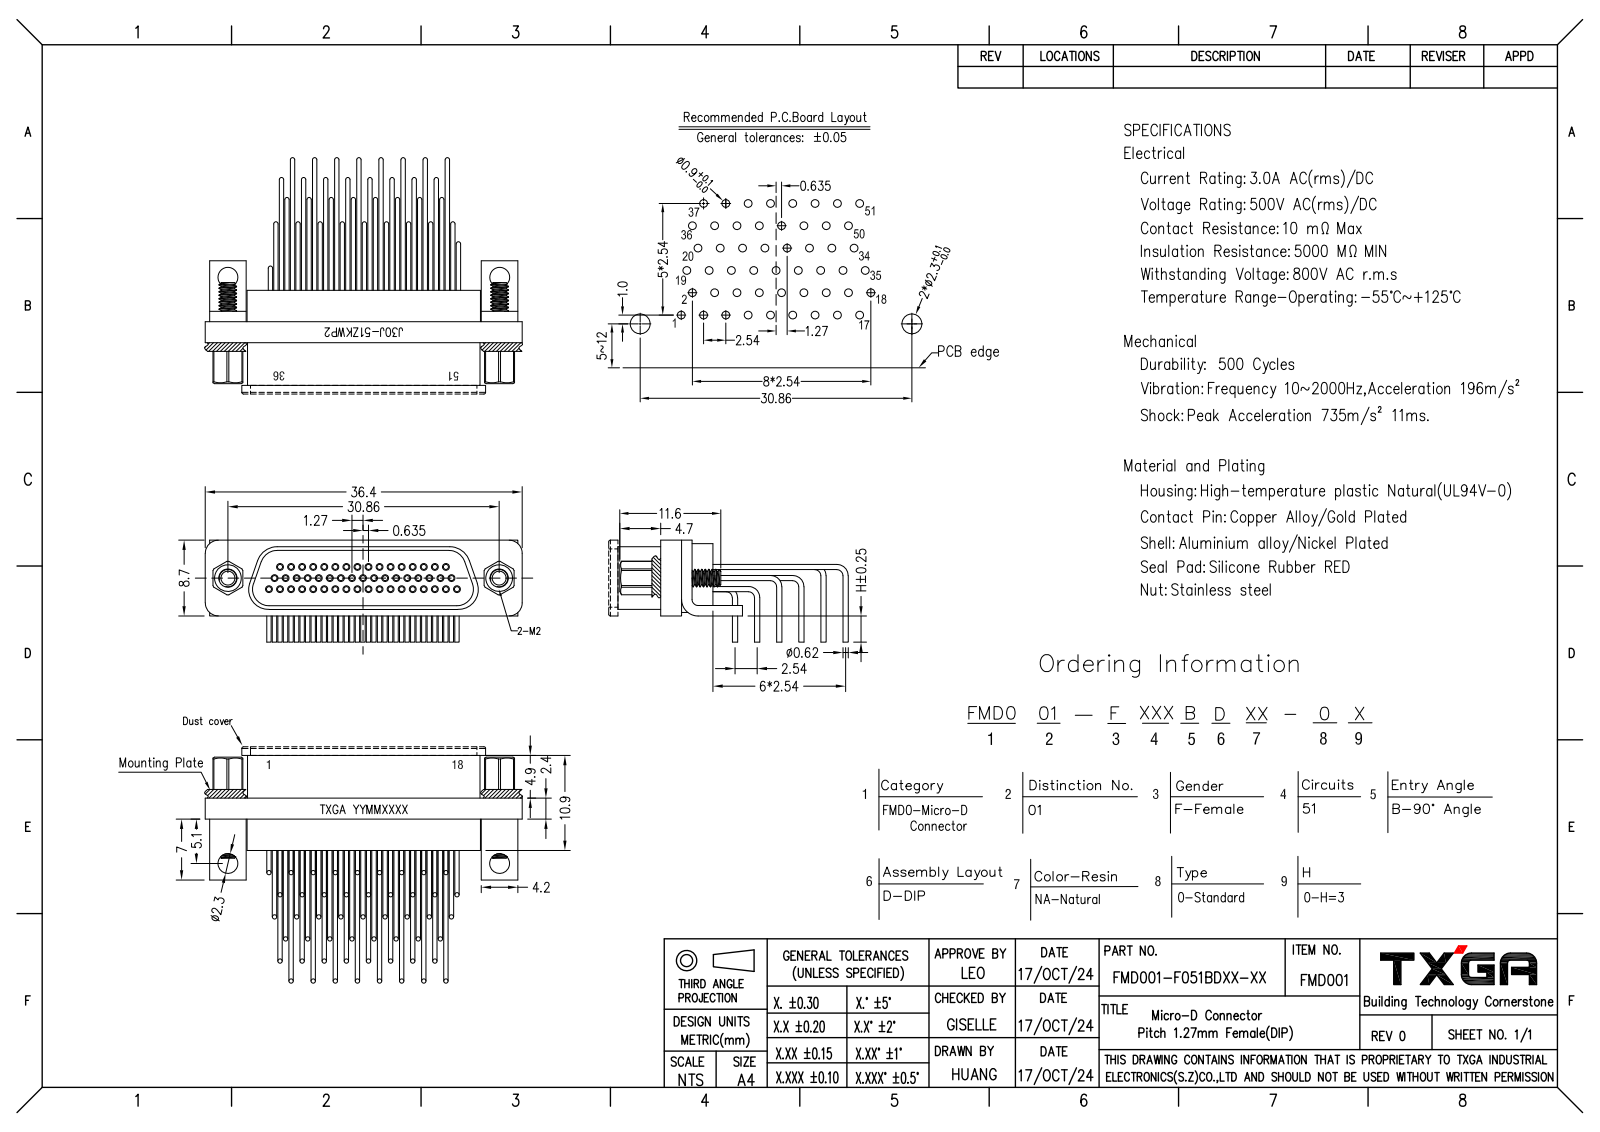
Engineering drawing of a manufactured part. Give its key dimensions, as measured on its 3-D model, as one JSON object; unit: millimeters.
{"part_name": "FMD001-F051BDNA-00", "step_written_by": "SolidWorks 2021 (CONFIG_CONTROL_DESIGN)", "units": "millimeters", "bodies": {"solids": 1, "faces": 1801, "planar": 701, "cylindrical": 568, "other": 532}, "overall_size": [36.4, 26.44, 11.7], "volume_mm3": 2184, "surface_area_mm2": 4432, "round_holes": [[0.6, 51], [1.6, 2], [1.8, 2], [2.3, 2], [3.2, 2]], "round_bosses_or_shafts": [[0.8, 51], [0.6, 51], [2, 2]], "partial_cylinders_radius": [[0.3, 12], [1.5, 4], [1.7, 4], [2, 4], [2.4, 4], [0.7, 1], [1.9, 1]], "face_to_face_distances": [0.7, 6, 0.75, 6.5, 1.45, 8.3, 0.4, 7.95, 7.25, 0.35], "hole_center_spacings": [1.27, 2.54, 2.2, 3.36, 5.08, 3.81, 7.62, 6.35]}
